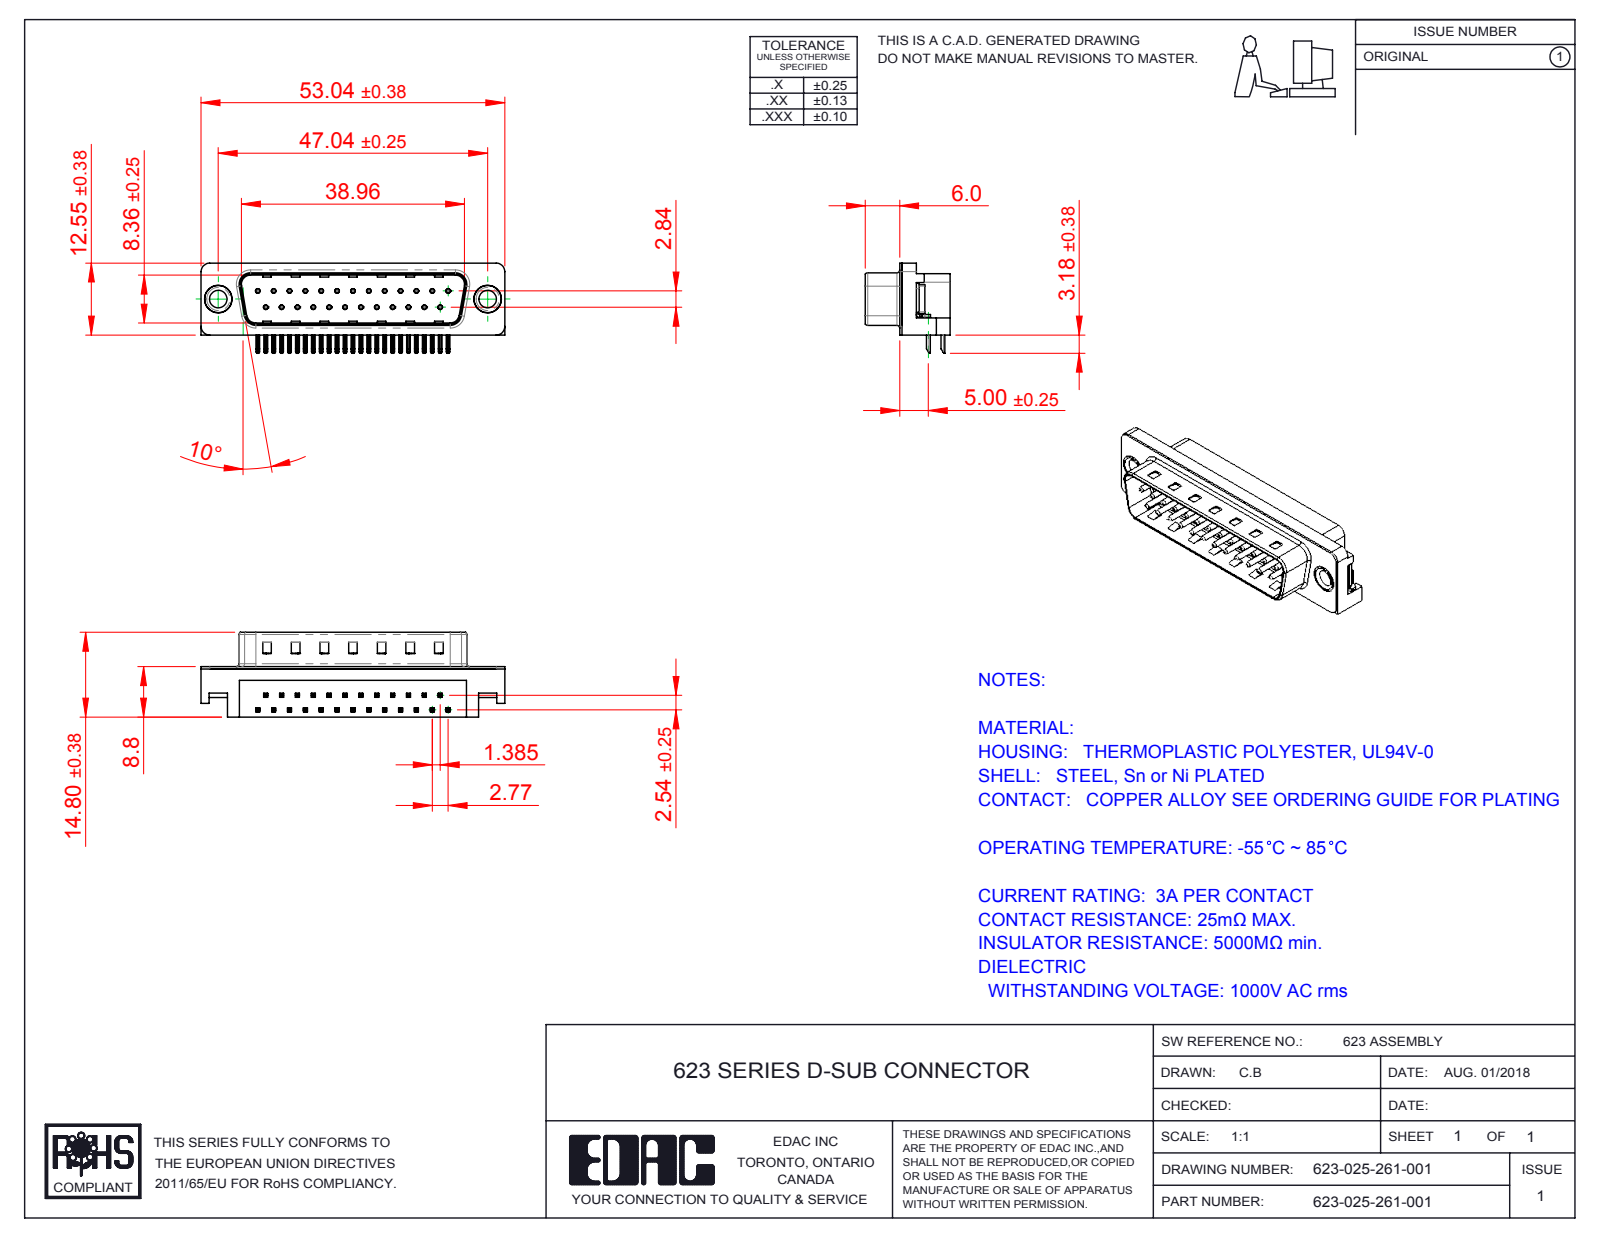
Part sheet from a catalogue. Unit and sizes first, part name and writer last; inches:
Units: inches
Overall size (bounding box): 2.088 × 0.619 × 0.583
Round holes (diameter × count): ⌀0.014 ×25, ⌀0.031 ×25, ⌀0.12 ×2, ⌀0.157 ×2, ⌀0.189 ×2, ⌀0.197 ×2
Round bosses / shafts (diameter × count): ⌀0.03 ×25, ⌀0.193 ×2, ⌀0.187 ×2, ⌀0.152 ×2
Partial cylindrical surfaces — rounded edges, fillets, slot ends (radius × count): R0.01 ×108, R0.005 ×50, R0.039 ×16, R0.02 ×9, R0.059 ×7, R0.035 ×4, R0.063 ×4, R0.079 ×4
Main face-to-face distances: 0.016, 0.331, 0.083, 0.067, 0.345, 0.412, 0.428, 0.407, 0.346, 0.232
Hole centre spacings: 0.124, 0.109, 0.436, 0.218, 0.327, 0.198, 0.545, 0.294
Volume: 0.288 in³ · Surface area: 10.37 in²
Bodies: 31 solids, 2213 faces (1405 planar, 631 cylindrical, 177 other)
Part name (STEP PRODUCT): 623 Housing_25 Socket; 623 Shell_25 Socket; 623 Thru Hole Rivet; 623 Non Board Mount (+3 more)
STEP written by: SolidWorks 2016 (CONFIG_CONTROL_DESIGN)
